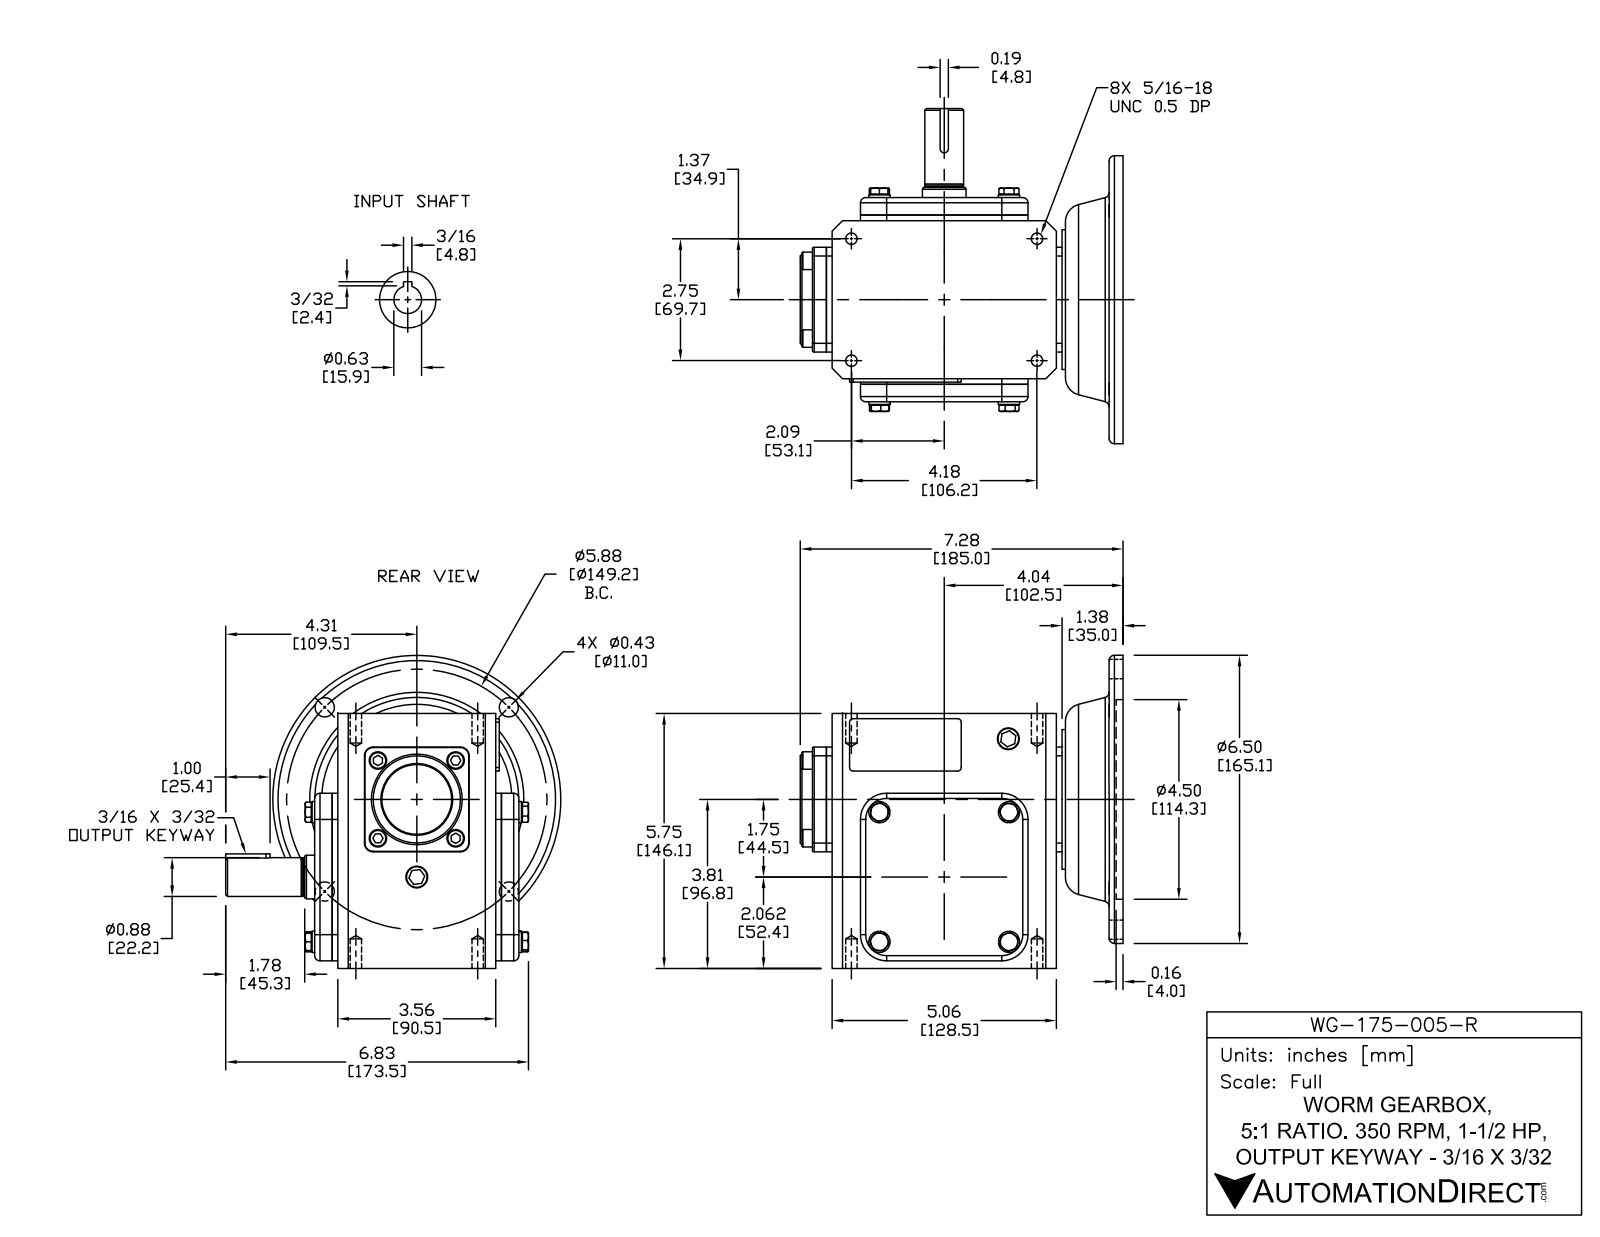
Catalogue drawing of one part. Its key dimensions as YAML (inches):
part_name: "WG-175-005-R"
step_written_by: "SolidWorks 2015 (CONFIG_CONTROL_DESIGN)"
units: inches
bodies: {solids: 43, faces: 613, planar: 312, cylindrical: 172, other: 129}
overall_size: [7.559, 7.283, 7.06]
volume: 131.9
surface_area: 366.4
round_holes:
  - {diameter: 0.257, count: 4}
  - {diameter: 0.406, count: 4}
  - {diameter: 0.512, count: 1}
  - {diameter: 0.625, count: 1}
  - {diameter: 0.984, count: 1}
  - {diameter: 1.181, count: 1}
  - {diameter: 1.457, count: 1}
  - {diameter: 1.575, count: 1}
  - {diameter: 3.543, count: 1}
  - {diameter: 4.5, count: 1}
round_bosses_or_shafts:
  - {diameter: 0.394, count: 8}
  - {diameter: 0.48, count: 4}
  - {diameter: 0.512, count: 2}
  - {diameter: 6.496, count: 1}
  - {diameter: 3.15, count: 1}
  - {diameter: 2.047, count: 1}
  - {diameter: 1.575, count: 1}
  - {diameter: 0.875, count: 1}
partial_cylinders:
  - {radius: 0.079, count: 8}
  - {radius: 0.118, count: 8}
  - {radius: 0.197, count: 4}
  - {radius: 0.591, count: 4}
  - {radius: 0.02, count: 2}
  - {radius: 0.039, count: 2}
  - {radius: 0.094, count: 1}
face_to_face_distances: [0.128, 3.819, 4.213, 0.394, 4.085, 3.691, 0.522, 0.315, 5.75, 6.693]
hole_center_spacings: [2.937, 4.154, 2.103, 2.75, 4.188, 4.354, 5.01, 5.875]
